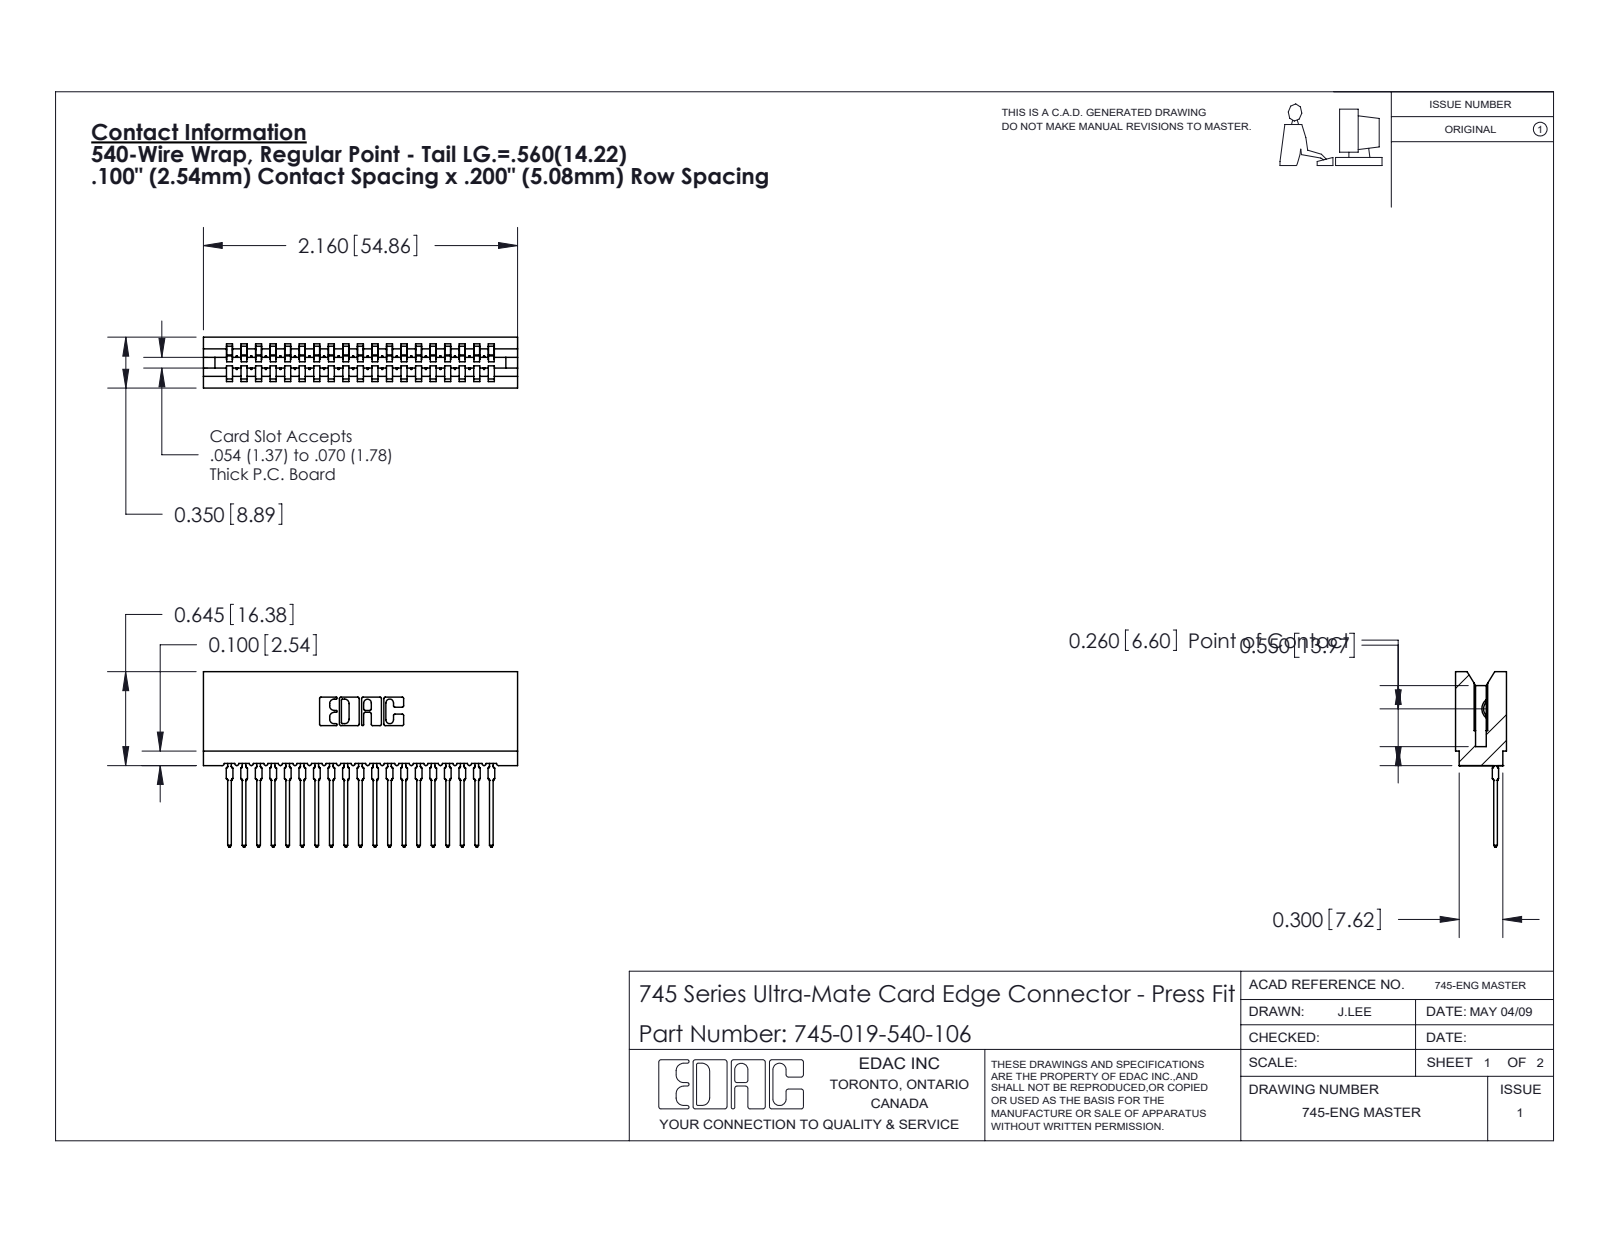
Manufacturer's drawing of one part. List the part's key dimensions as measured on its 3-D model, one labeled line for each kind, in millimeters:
Part name (STEP PRODUCT): 745-292-001_540; 745 Part_Insulator Option - 06; 745-019-540-106
STEP written by: SolidWorks 2020 (CONFIG_CONTROL_DESIGN)
Units: millimetres
Bodies: 20 solids, 2224 faces (1329 planar, 401 cylindrical, 494 other)
Overall size (bounding box): 54.9 × 30.6 × 8.9
Volume: 4 930 mm³ · Surface area: 8 961 mm²
Partial cylindrical surfaces — rounded edges, fillets, slot ends (radius × count): R0.4 ×38, R0.5 ×38, R0.3 ×22, R0.2 ×6, R0.8 ×6, R0.1 ×4, R0.3 ×4, R0.7 ×3
Main face-to-face distances: 2.5, 5.1, 8.9, 12.7, 10.2, 3.5, 5.4, 15.2, 7.6, 1.1
